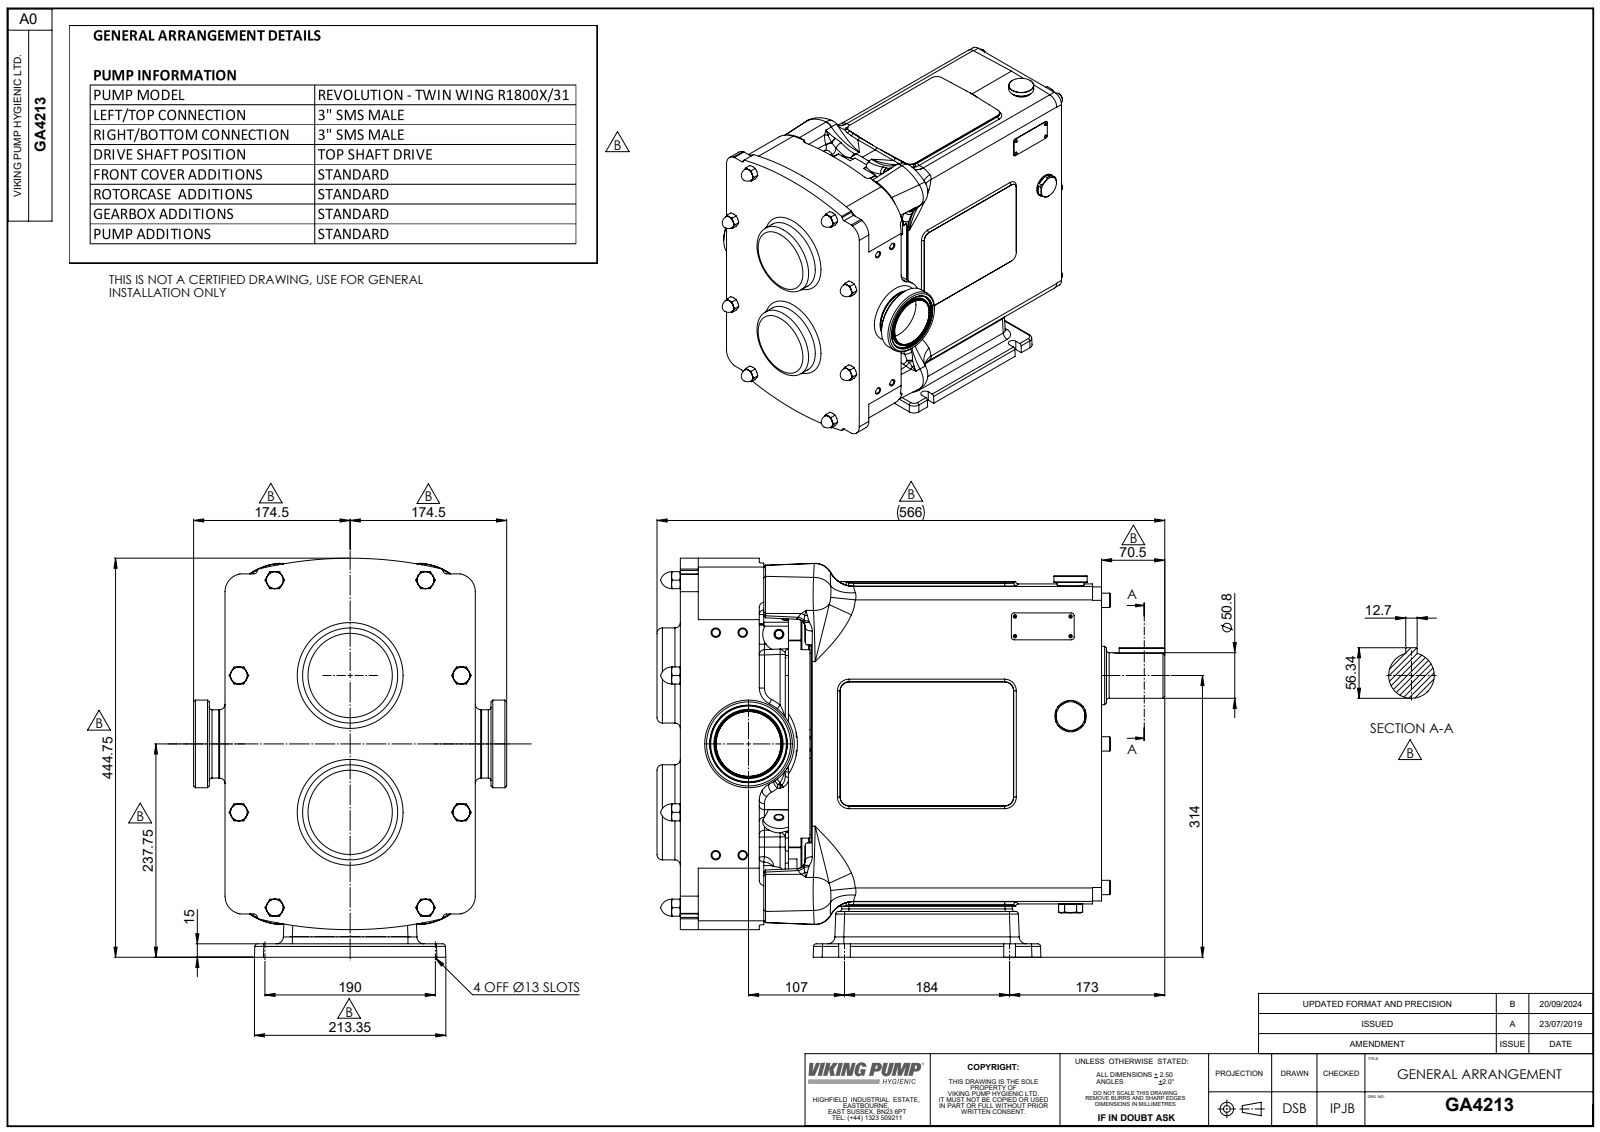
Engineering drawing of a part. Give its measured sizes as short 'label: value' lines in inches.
name: GA4213; Copy of Z94-5101-55 - 3 INCH SMS681^GA4213; Copy of R1800 CPP H TSD^GA4213
written by: SolidWorks 2023 (AUTOMOTIVE_DESIGN)
unit: in
bodies: 4 solids, 1737 faces (528 planar, 419 cylindrical, 790 other)
size: 22.283 × 17.51 × 13.74
volume: 2 280 in³; area: 1 908 in²
holes: 4× ⌀0.335, 2× ⌀5.866, 1× ⌀1.378, 1× ⌀2.708, 1× ⌀2.843, 1× ⌀3.386
bosses: 10× ⌀0.551, 10× ⌀0.315, 6× ⌀0.63, 4× ⌀0.709, 2× ⌀7.362, 2× ⌀5.512, 2× ⌀4.173, 2× ⌀1.24
rounds: 44× R0.118, 36× R0.236, 30× R0.394, 24× R0.008, 16× R0.039, 16× R0.197, 14× R0.157, 10× R0.315
face distances: 7.48, 18.484, 0.118, 7.598, 13.74, 4.744, 1.634, 1.752, 9.232, 9.35
hole spacings: 1.181, 4.889, 5.089, 9.764, 9.835, 6.004
